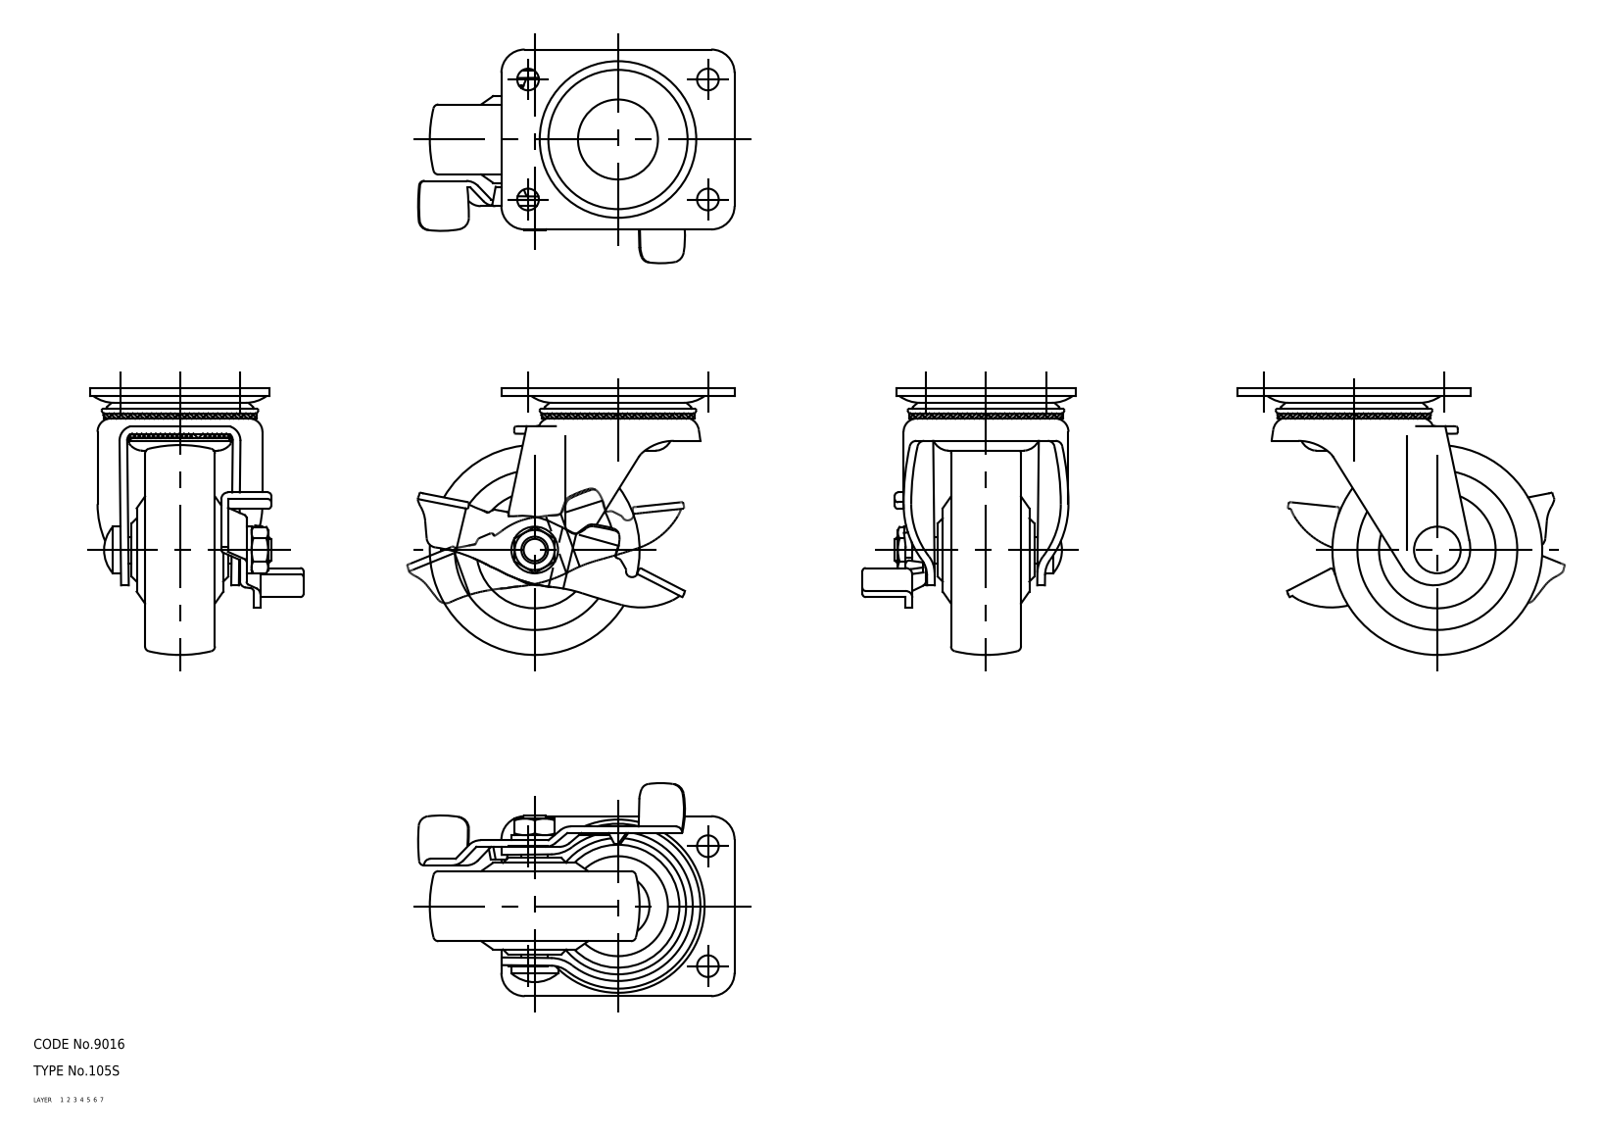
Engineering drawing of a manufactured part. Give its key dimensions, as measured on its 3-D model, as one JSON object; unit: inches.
{"part_name": "lever; wheel; mounting plate; main shaft (+2 more)", "step_written_by": "CADfix (AUTOMOTIVE_DESIGN)", "units": "inches", "bodies": {"solids": 6, "faces": 339, "planar": 0, "cylindrical": 0, "other": 339}, "overall_size": [3.746, 3.15, 2.524], "volume_in3": 6.427, "surface_area_in2": 61.17}
